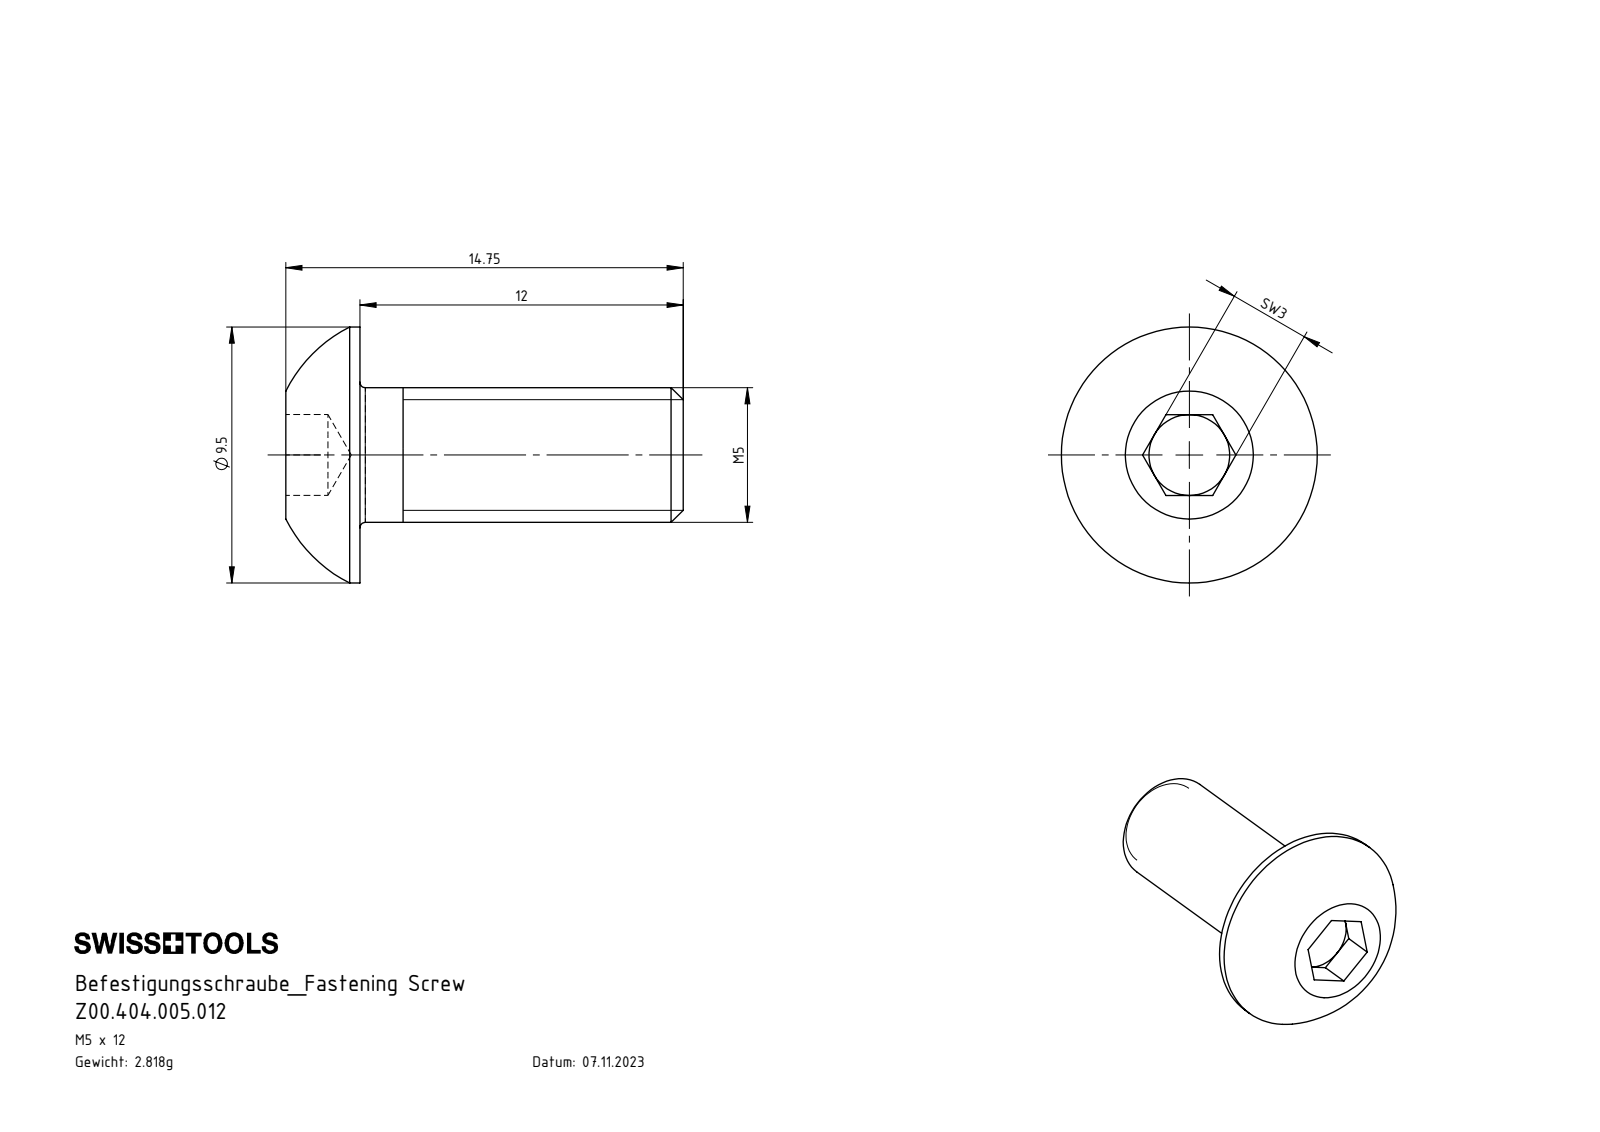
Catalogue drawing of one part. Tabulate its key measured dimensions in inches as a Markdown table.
| quantity | value |
| --- | --- |
| part name | Z00.404.005.012 |
| STEP written by | SolidWorks 2022 (AUTOMOTIVE_DESIGN) |
| units | inches |
| bodies | 1 solid, 27 faces (15 planar, 4 cylindrical, 8 other) |
| overall size | 0.581 × 0.374 × 0.374 |
| volume | 0.022 in³ |
| surface area | 0.587 in² |
| round bosses / shafts (diameter × count) | 0.374 × 1, 0.197 × 1 |
| main face-to-face distances | 0.472, 0.108, 0.581, 0.118, 0.061, 0.047, 0.519 |
